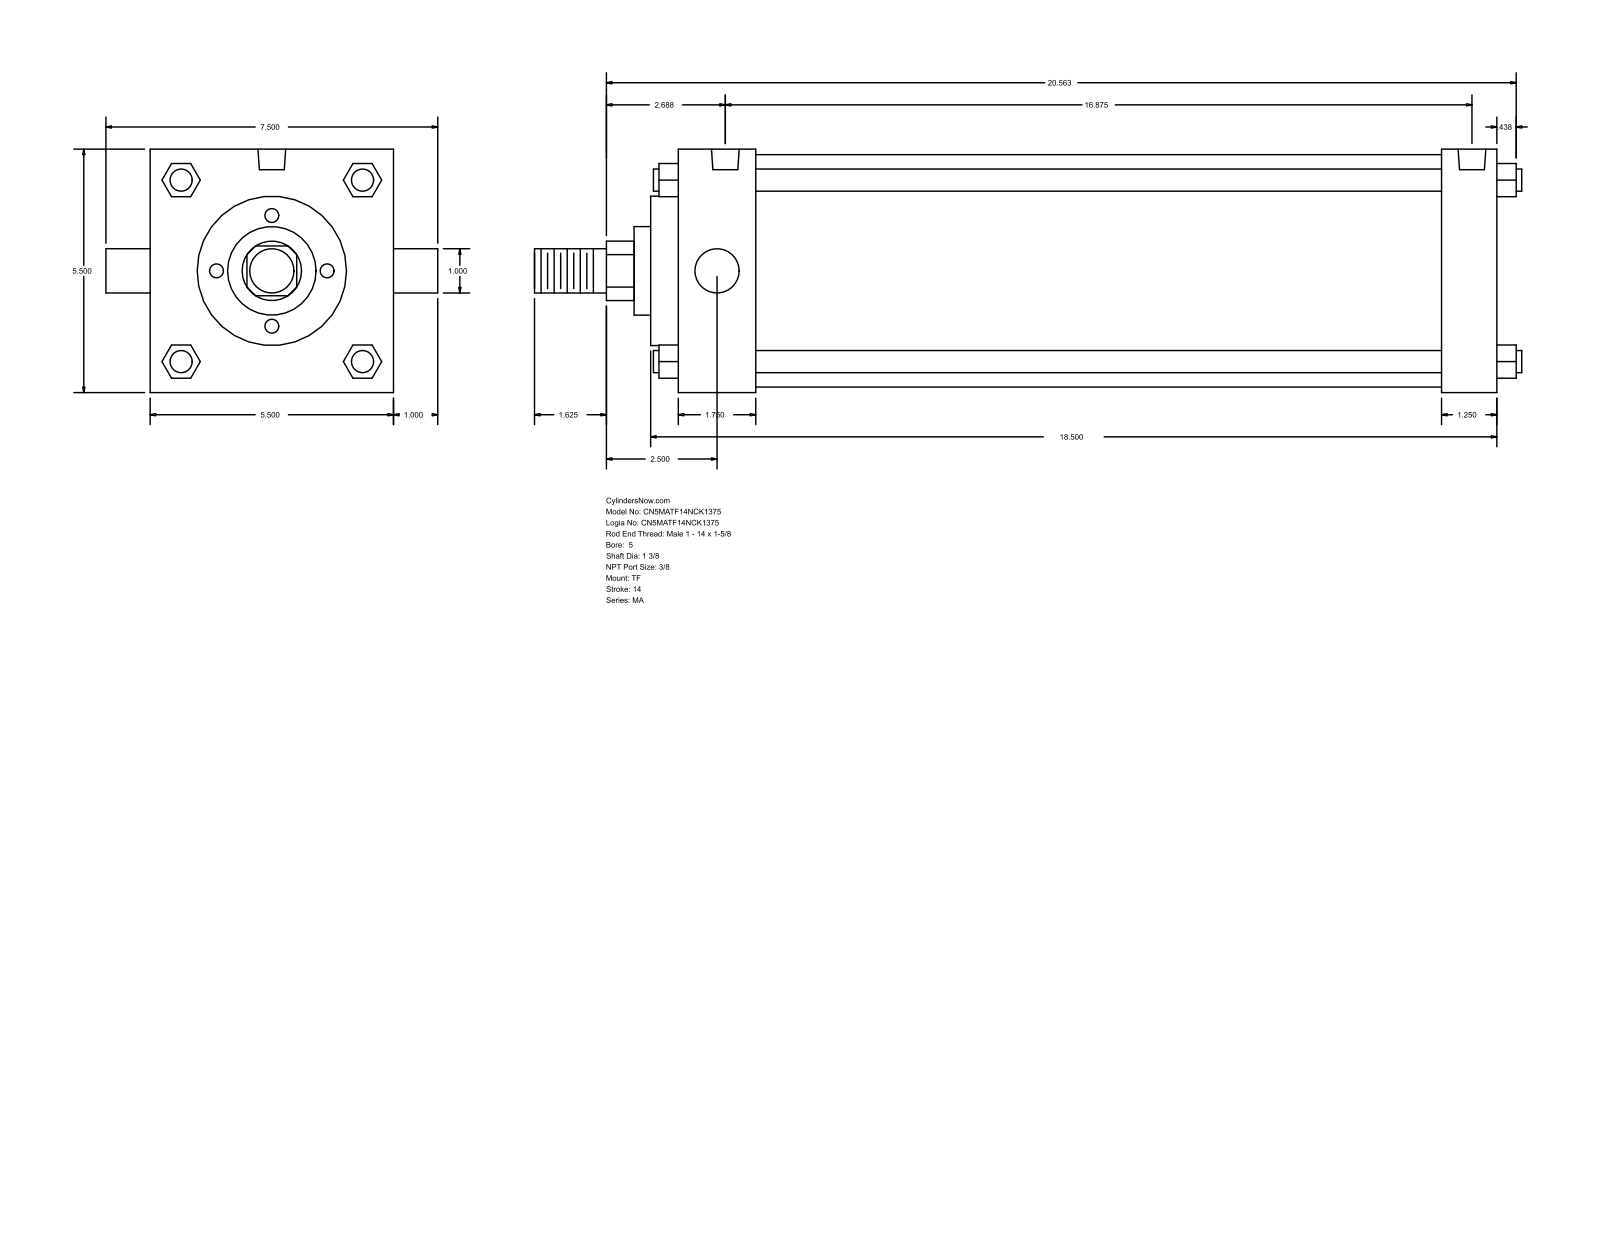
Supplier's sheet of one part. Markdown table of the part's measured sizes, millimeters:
| quantity | value |
| --- | --- |
| part name | MA_TF__0500_1.375 |
| STEP written by | GSSL Pune (CONFIG_CONTROL_DESIGN) |
| units | millimeters |
| bodies | 0 solids, 122 faces (93 planar, 29 cylindrical, 0 other) |
| overall size | 566.74 × 190.5 × 139.7 |
| round holes (diameter × count) | 11.11 × 3, 15.93 × 2 |
| round bosses / shafts (diameter × count) | 12.7 × 4, 25.4 × 2, 133.35 × 1, 85.72 × 1, 50.8 × 1, 34.92 × 1 |
| partial cylindrical surfaces (radius × count) | 17.06 × 1 |
| main face-to-face distances | 139.7, 469.91, 438.16, 31.75, 44.45, 393.71, 425.46, 15.87, 60.32, 454.03 |
| hole center spacings | 4.77, 423.86, 419.09, 428.63 |
